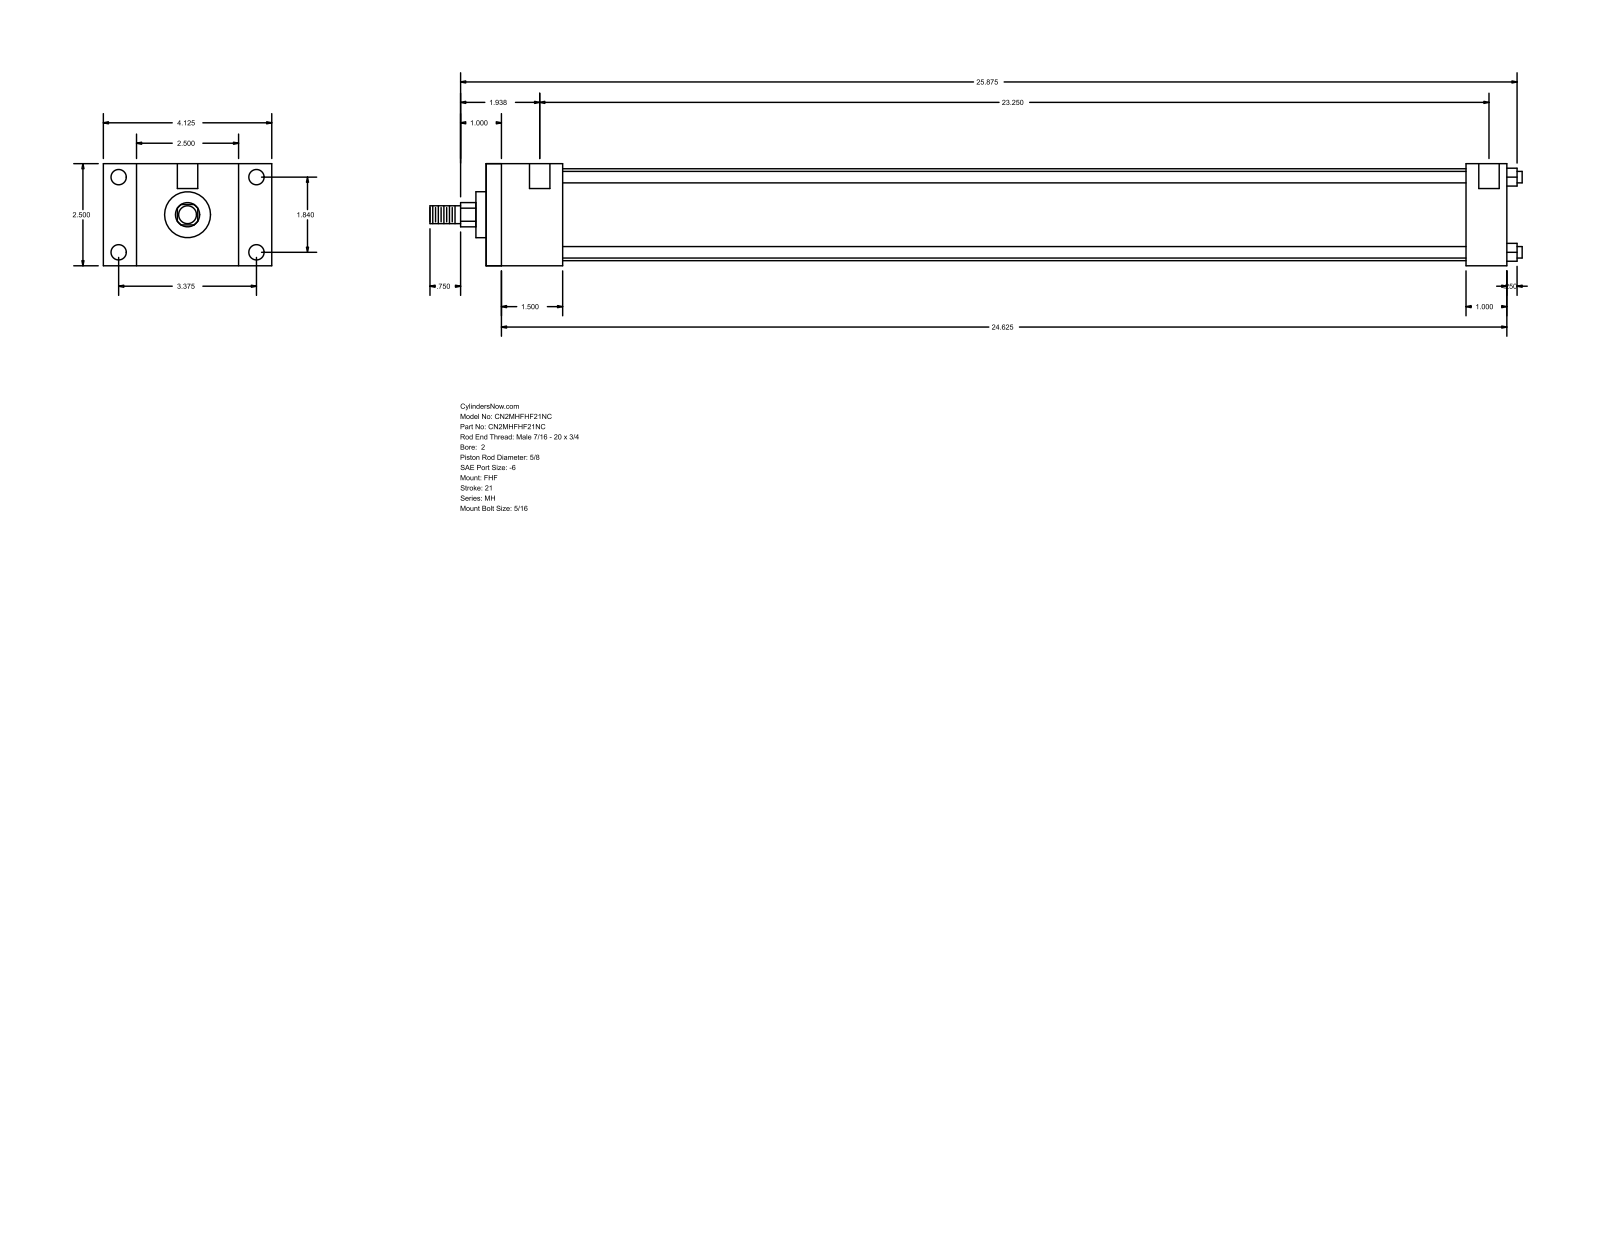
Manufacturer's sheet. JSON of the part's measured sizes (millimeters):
{"part_name": "MH_FHF__0200_0.625", "step_written_by": "GSSL Pune (CONFIG_CONTROL_DESIGN)", "units": "millimeters", "bodies": {"solids": 0, "faces": 88, "planar": 60, "cylindrical": 28, "other": 0}, "overall_size": [679.45, 104.78, 63.5], "round_holes": [[5.56, 4], [9.53, 4], [12.7, 2]], "round_bosses_or_shafts": [[7.14, 4], [57.15, 1], [28.57, 1], [15.88, 1], [11.11, 1]], "partial_cylinders_radius": [[7.54, 1]], "face_to_face_distances": [63.5, 47.62, 635, 587.38, 20.64, 84.14, 104.78, 25.4, 609.6, 561.98], "hole_center_spacings": [46.74, 85.72, 97.63, 598.49, 3.18, 4.76, 590.55, 593.73]}
